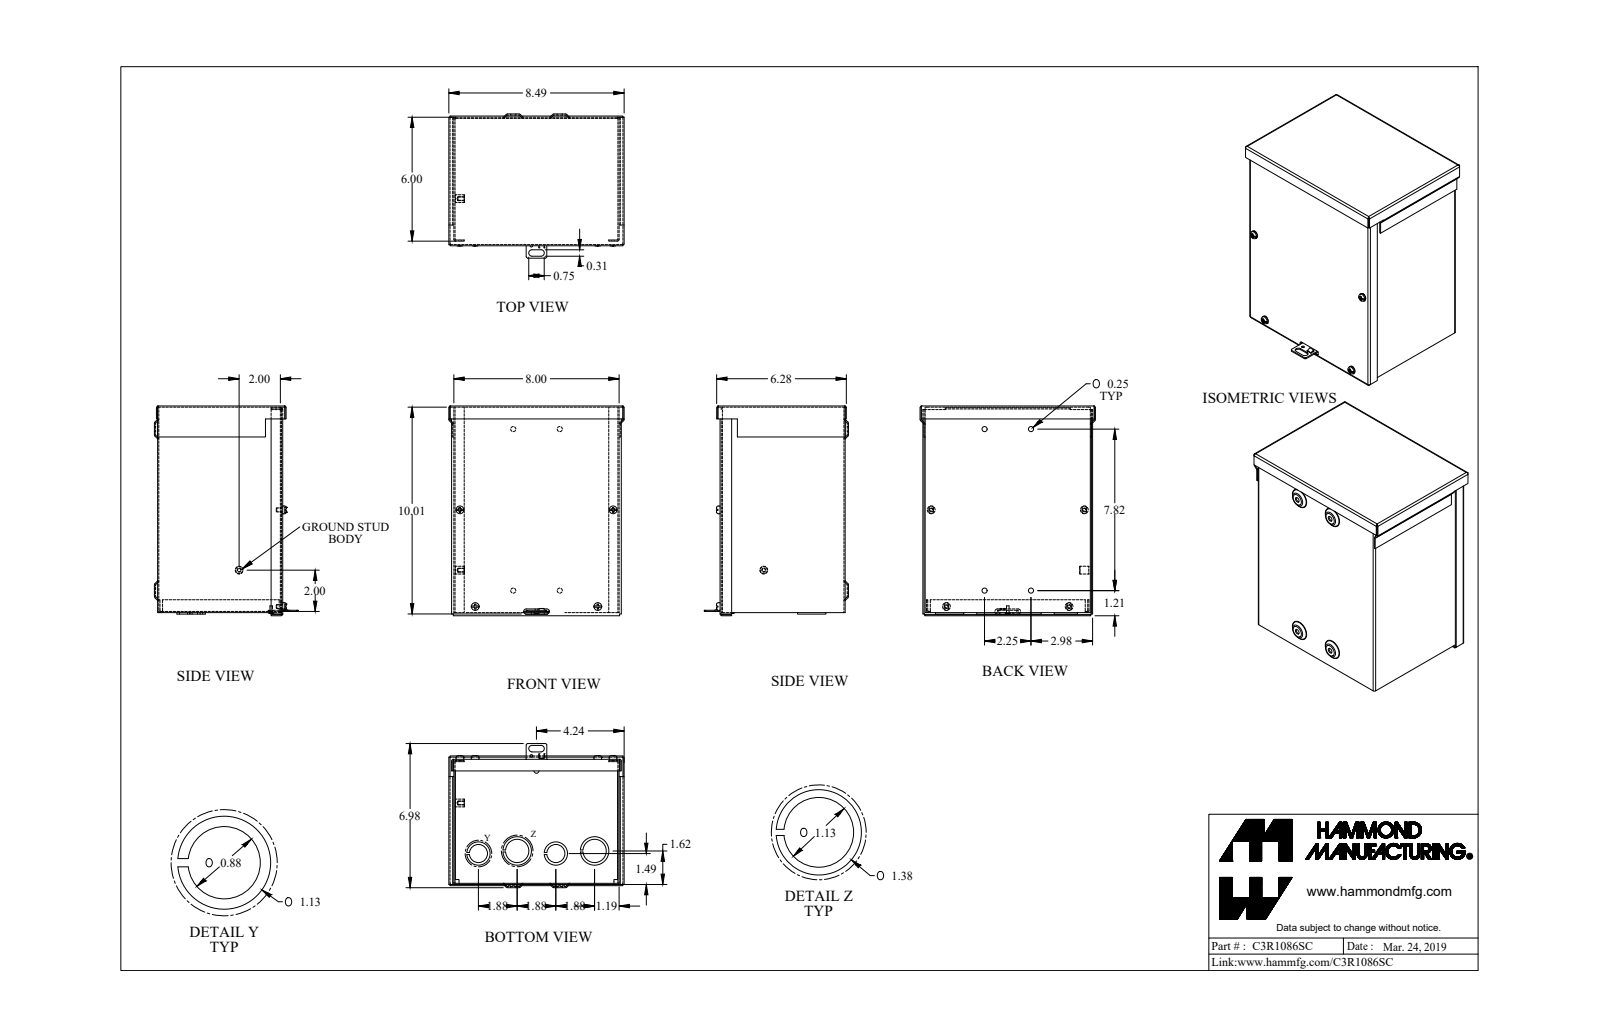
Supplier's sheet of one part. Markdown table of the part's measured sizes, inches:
| quantity | value |
| --- | --- |
| part name | C3R1086SC_Default |
| STEP written by | SolidWorks 2019 (CONFIG_CONTROL_DESIGN) |
| units | inches |
| bodies | 11 solids, 424 faces (223 planar, 115 cylindrical, 86 other) |
| overall size | 10.151 × 8.489 × 6.977 |
| volume | 25.53 in³ |
| surface area | 903.3 in² |
| round holes (diameter × count) | 0.17 × 4, 0.25 × 4, 0.125 × 1, 0.137 × 1, 0.156 × 1, 0.875 × 1, 0.875 × 1, 1.125 × 1, 1.125 × 1 |
| round bosses / shafts (diameter × count) | 0.375 × 4, 0.19 × 4, 1.125 × 2, 1.375 × 1, 1.375 × 1, 0.375 × 1, 0.125 × 1 |
| partial cylindrical surfaces (radius × count) | 0.029 × 21, 0.086 × 21, 0.109 × 8, 0.125 × 8, 0.156 × 2 |
| main face-to-face distances | 0.057, 6, 7.943, 5.943, 6.057, 8, 7.886, 0.057, 9.886, 9.943 |
| hole center spacings | 4.685, 6.215, 1.88, 1.998, 2.25, 3.75, 4.165, 4.736 |
